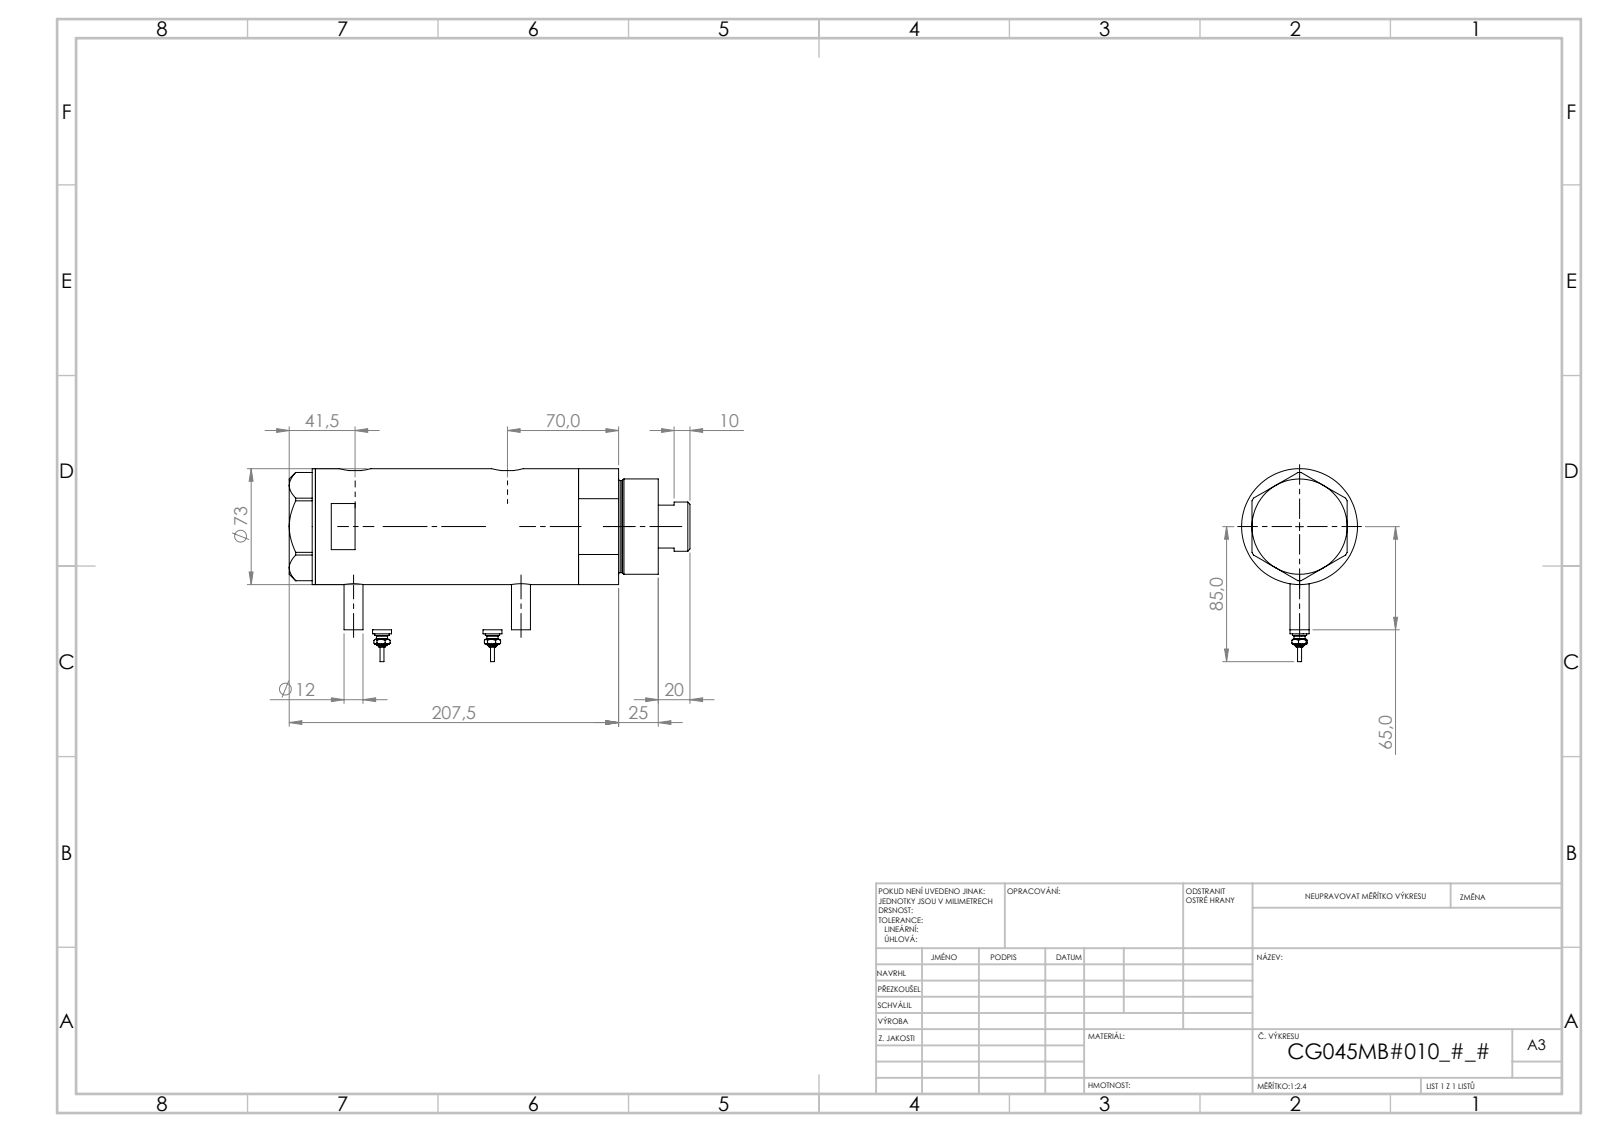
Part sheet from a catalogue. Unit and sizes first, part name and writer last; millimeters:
Units: millimetres
Overall size (bounding box): 252.5 × 121.5 × 73
Round holes (diameter × count): ⌀12.5 ×2, ⌀13.16 ×2, ⌀10.5 ×1, ⌀32 ×1, ⌀33.5 ×1, ⌀45 ×1, ⌀48 ×1, ⌀64 ×1
Round bosses / shafts (diameter × count): ⌀12 ×4, ⌀9 ×2, ⌀7 ×2, ⌀4.5 ×2, ⌀2.5 ×2, ⌀73 ×1, ⌀60 ×1, ⌀58 ×1
Partial cylindrical surfaces — rounded edges, fillets, slot ends (radius × count): R10 ×2
Main face-to-face distances: 95, 121, 26, 16.5, 42.5, 137.5, 2, 216, 232.5, 190
Hole centre spacings: 1, 8.5, 96, 97, 104.5, 105.5
Volume: 923 606 mm³ · Surface area: 153 363 mm²
Bodies: 6 solids, 212 faces (77 planar, 71 cylindrical, 64 other)
Part name (STEP PRODUCT): V270CG_FRONT; Switch; V270CG_BACK; V270CG_MIDDLE (+1 more)
STEP written by: SolidWorks 2019 (CONFIG_CONTROL_DESIGN)
